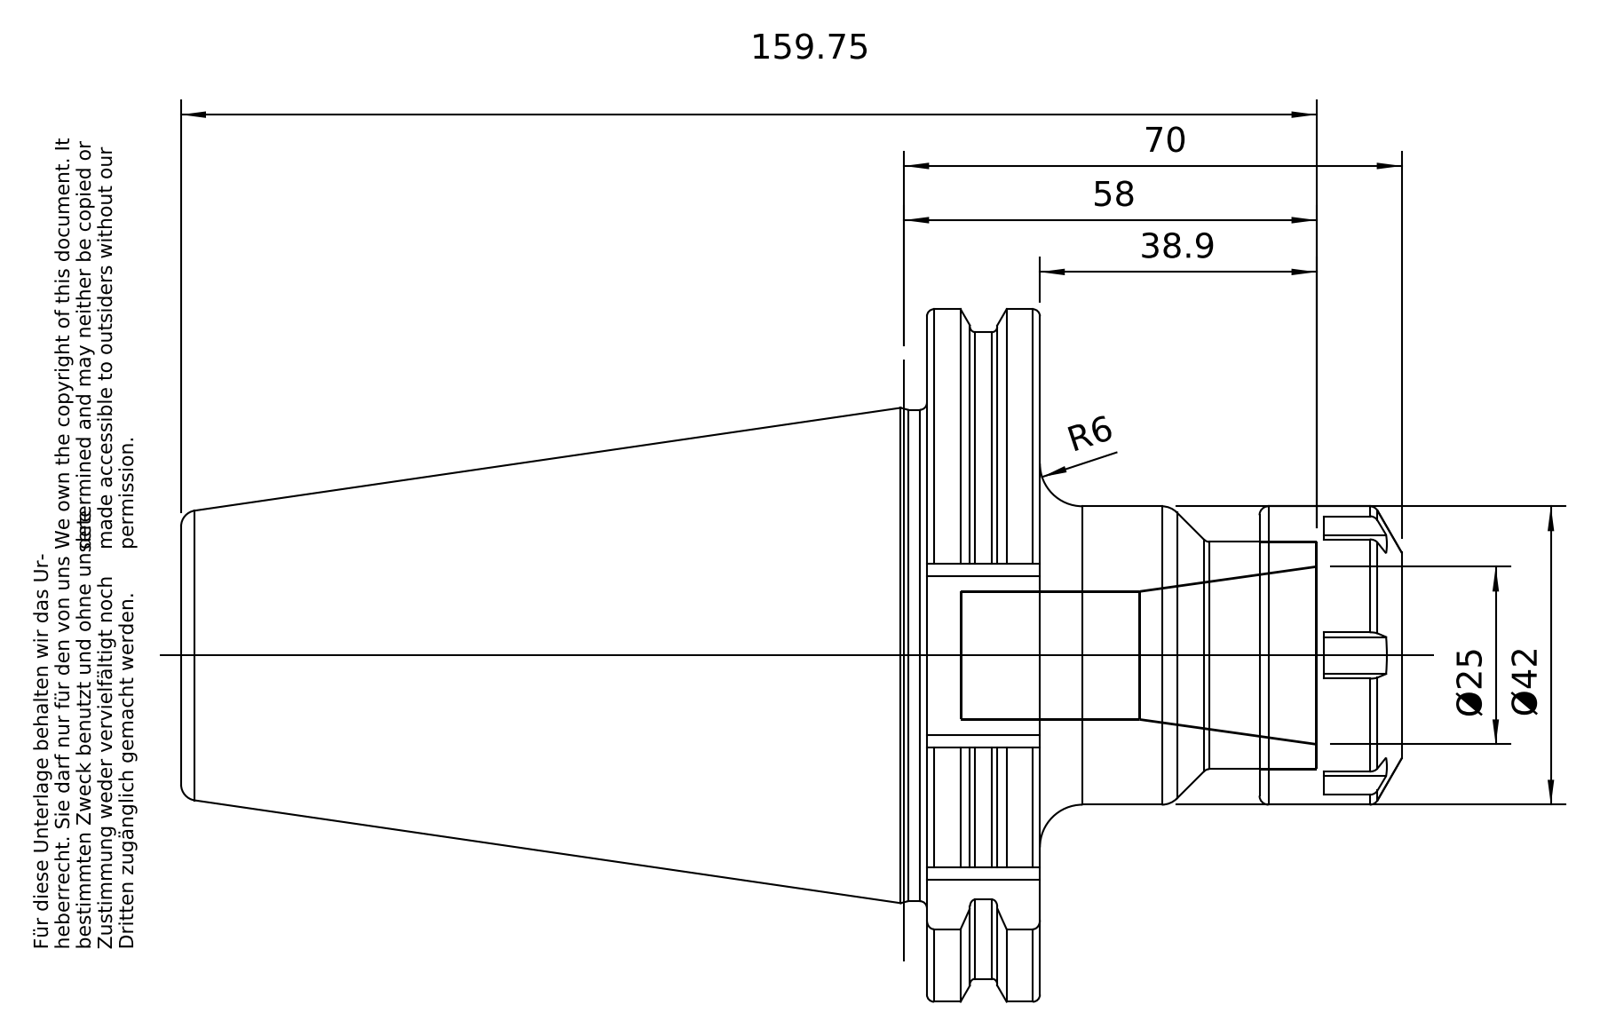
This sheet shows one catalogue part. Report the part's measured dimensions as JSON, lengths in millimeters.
{"part_name": "50-320-25; 83-912-25; 50-320-25_ASM", "step_written_by": "PRO/ENGINEER BY PARAMETRIC TECHNOLOGY CORPORATION, 2010430 (CONFIG_CONTROL_DESIGN)", "units": "millimeters", "bodies": {"solids": 2, "faces": 147, "planar": 41, "cylindrical": 32, "other": 74}, "overall_size": [171.6, 97.47, 94], "volume_mm3": 394034, "surface_area_mm2": 54522, "round_holes": [[18, 1], [20.75, 1], [25.01, 1], [25.7, 1]], "round_bosses_or_shafts": [[91, 1], [69.15, 1], [42, 1], [32, 1], [24.01, 1]], "partial_cylinders_radius": [[1.75, 5], [48.74, 1]], "face_to_face_distances": [15.85, 46.8, 30.95, 66.8, 50.95, 20, 104.8, 120.65, 151.6, 171.6]}
